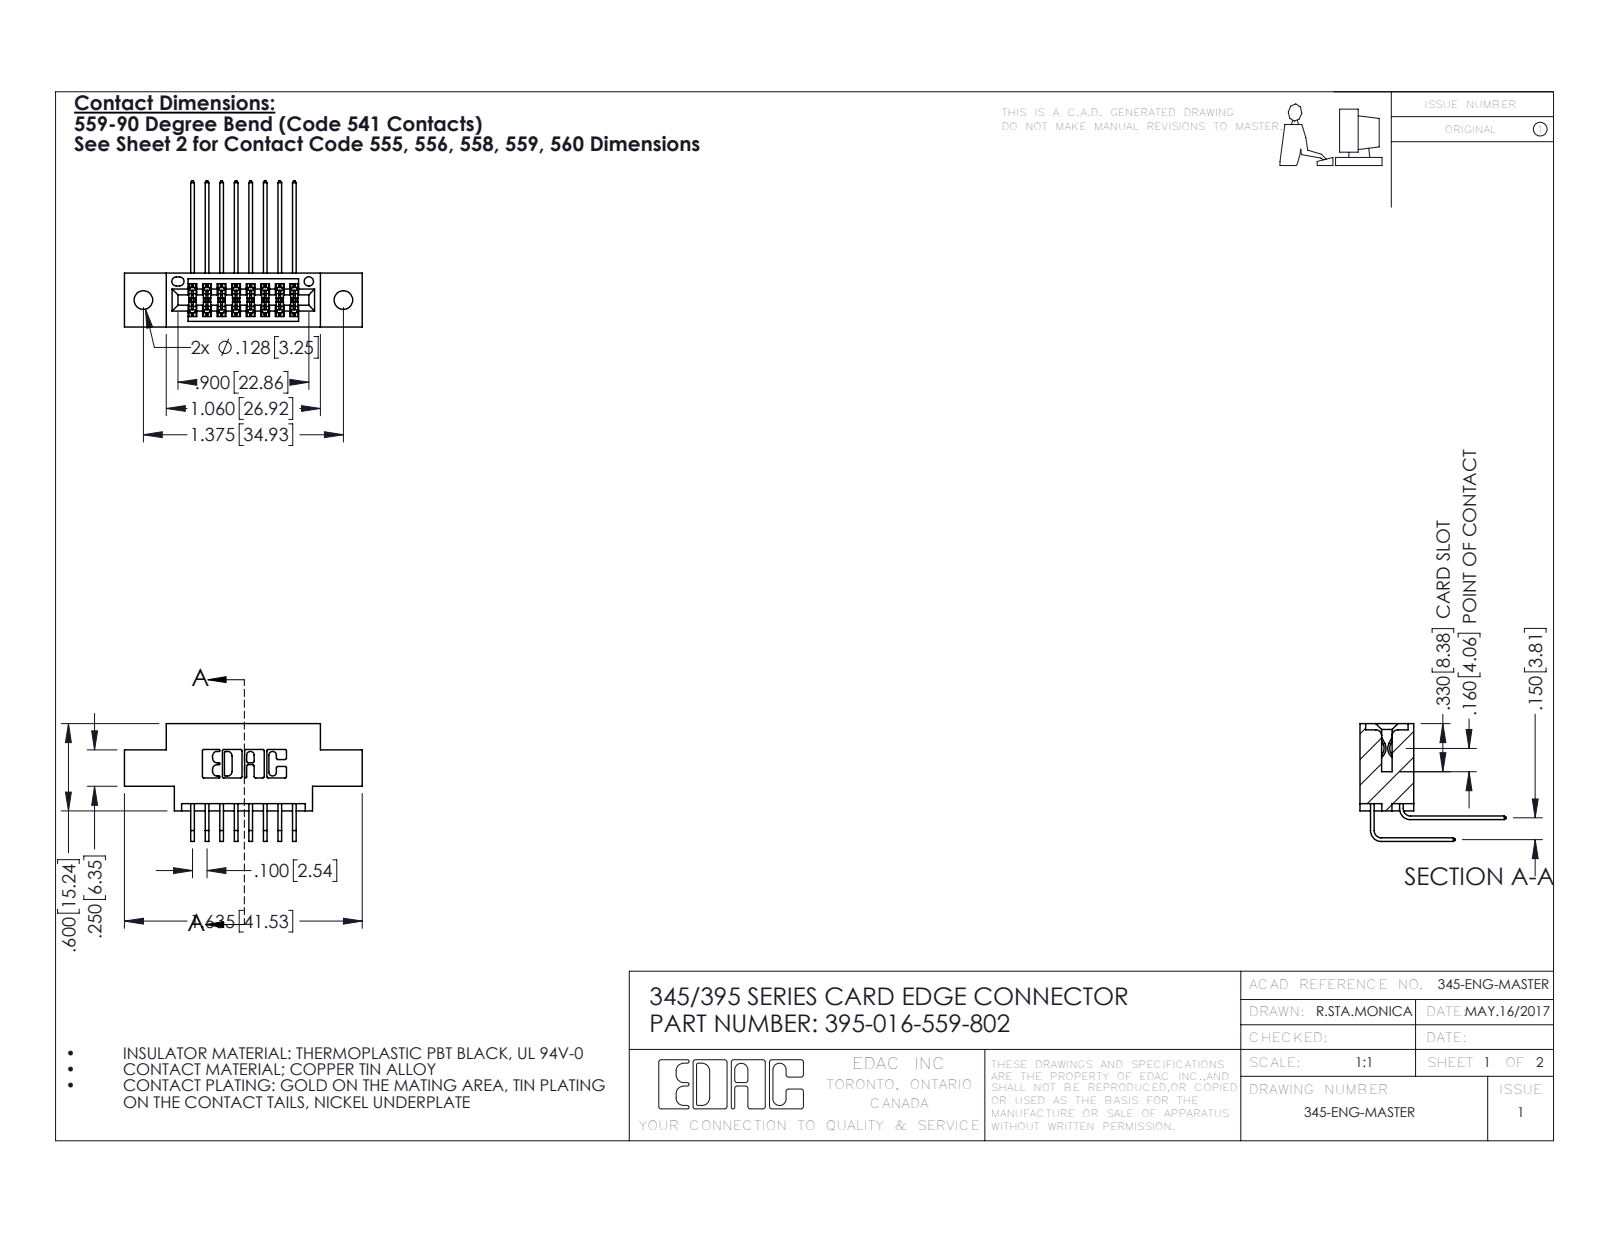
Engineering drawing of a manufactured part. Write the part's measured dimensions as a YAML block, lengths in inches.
part_name: "345-292-001_559 Tail - 2; 395-016-559-802; 345-292-001_558 559 Tail - 1; 345 Part_0.170 Offset - 0.128 Dia"
step_written_by: "SolidWorks 2016 (CONFIG_CONTROL_DESIGN)"
units: inches
bodies: {solids: 17, faces: 962, planar: 644, cylindrical: 318, other: 0}
overall_size: [1.635, 1.005, 0.809]
volume: 0.223
surface_area: 7.839
round_holes:
  - {diameter: 0.128, count: 2}
  - {diameter: 0.064, count: 1}
partial_cylinders:
  - {radius: 0.006, count: 25}
  - {radius: 0.01, count: 22}
  - {radius: 0.007, count: 6}
  - {radius: 0.031, count: 6}
  - {radius: 0.026, count: 3}
  - {radius: 0.014, count: 2}
  - {radius: 0.019, count: 2}
  - {radius: 0.022, count: 2}
face_to_face_distances: [0.37, 0.2, 0.072, 0.298, 0.1, 0.15, 0.098, 0.272, 0.025, 0.175]
hole_center_spacings: [0.27, 1.144, 1.375]
